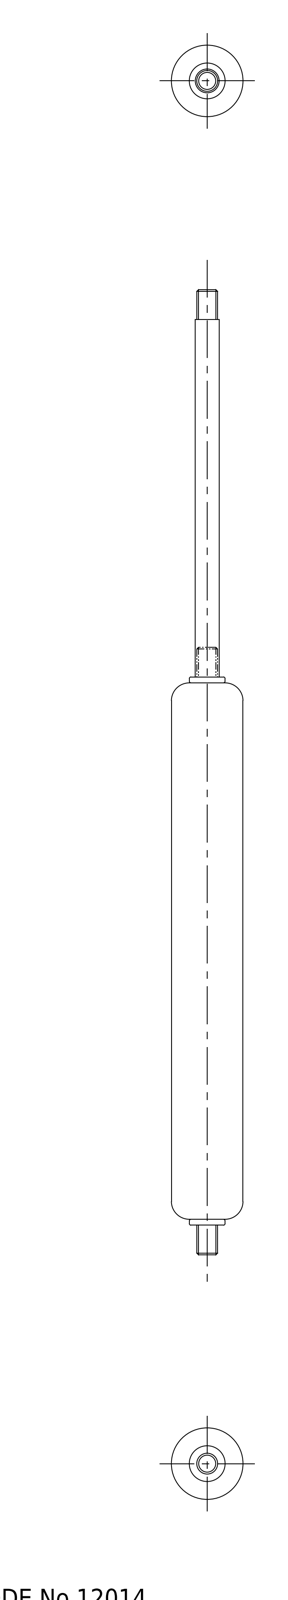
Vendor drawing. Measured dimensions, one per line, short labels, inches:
name: rod; TM_278_60_100_30211_36
written by: CADfix (AUTOMOTIVE_DESIGN)
unit: in
bodies: 2 solids, 36 faces (0 planar, 0 cylindrical, 36 other)
size: 6.378 × 0.472 × 0.472
volume: 0.67 in³; area: 6.932 in²
